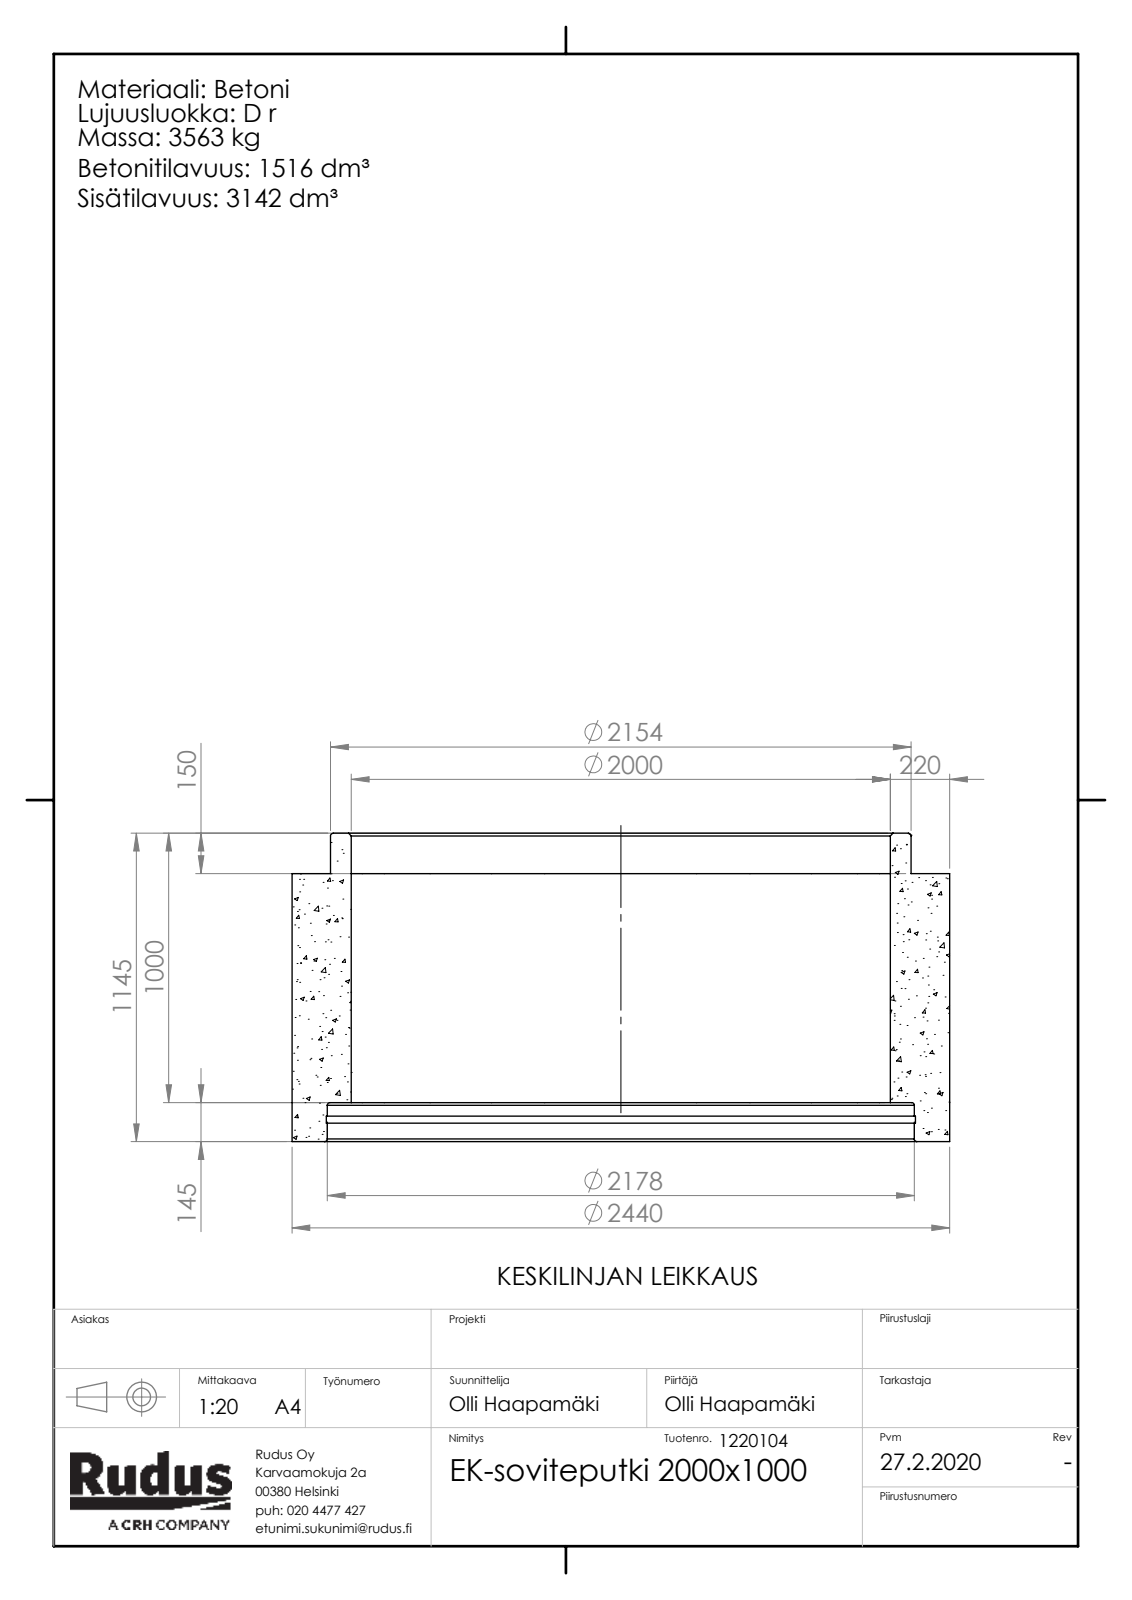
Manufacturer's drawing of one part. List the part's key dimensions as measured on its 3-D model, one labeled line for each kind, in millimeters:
Part name (STEP PRODUCT): EK-osa-putkirunko; Rudus 1220104 EK-soviteputki 2000x1000
STEP written by: SolidWorks 2019 (CONFIG_CONTROL_DESIGN)
Units: millimetres
Bodies: 1 solid, 107 faces (9 planar, 12 cylindrical, 86 other)
Overall size (bounding box): 2440 × 2440 × 1145
Volume: 1 516 000 000 mm³ · Surface area: 18 920 000 mm²
Round holes (diameter × count): ⌀2000 ×1, ⌀2178 ×1, ⌀2186 ×1
Round bosses / shafts (diameter × count): ⌀2440 ×1, ⌀2154 ×1
Main face-to-face distances: 995, 145, 850, 1145, 1000, 150, 69, 76, 926, 1076
